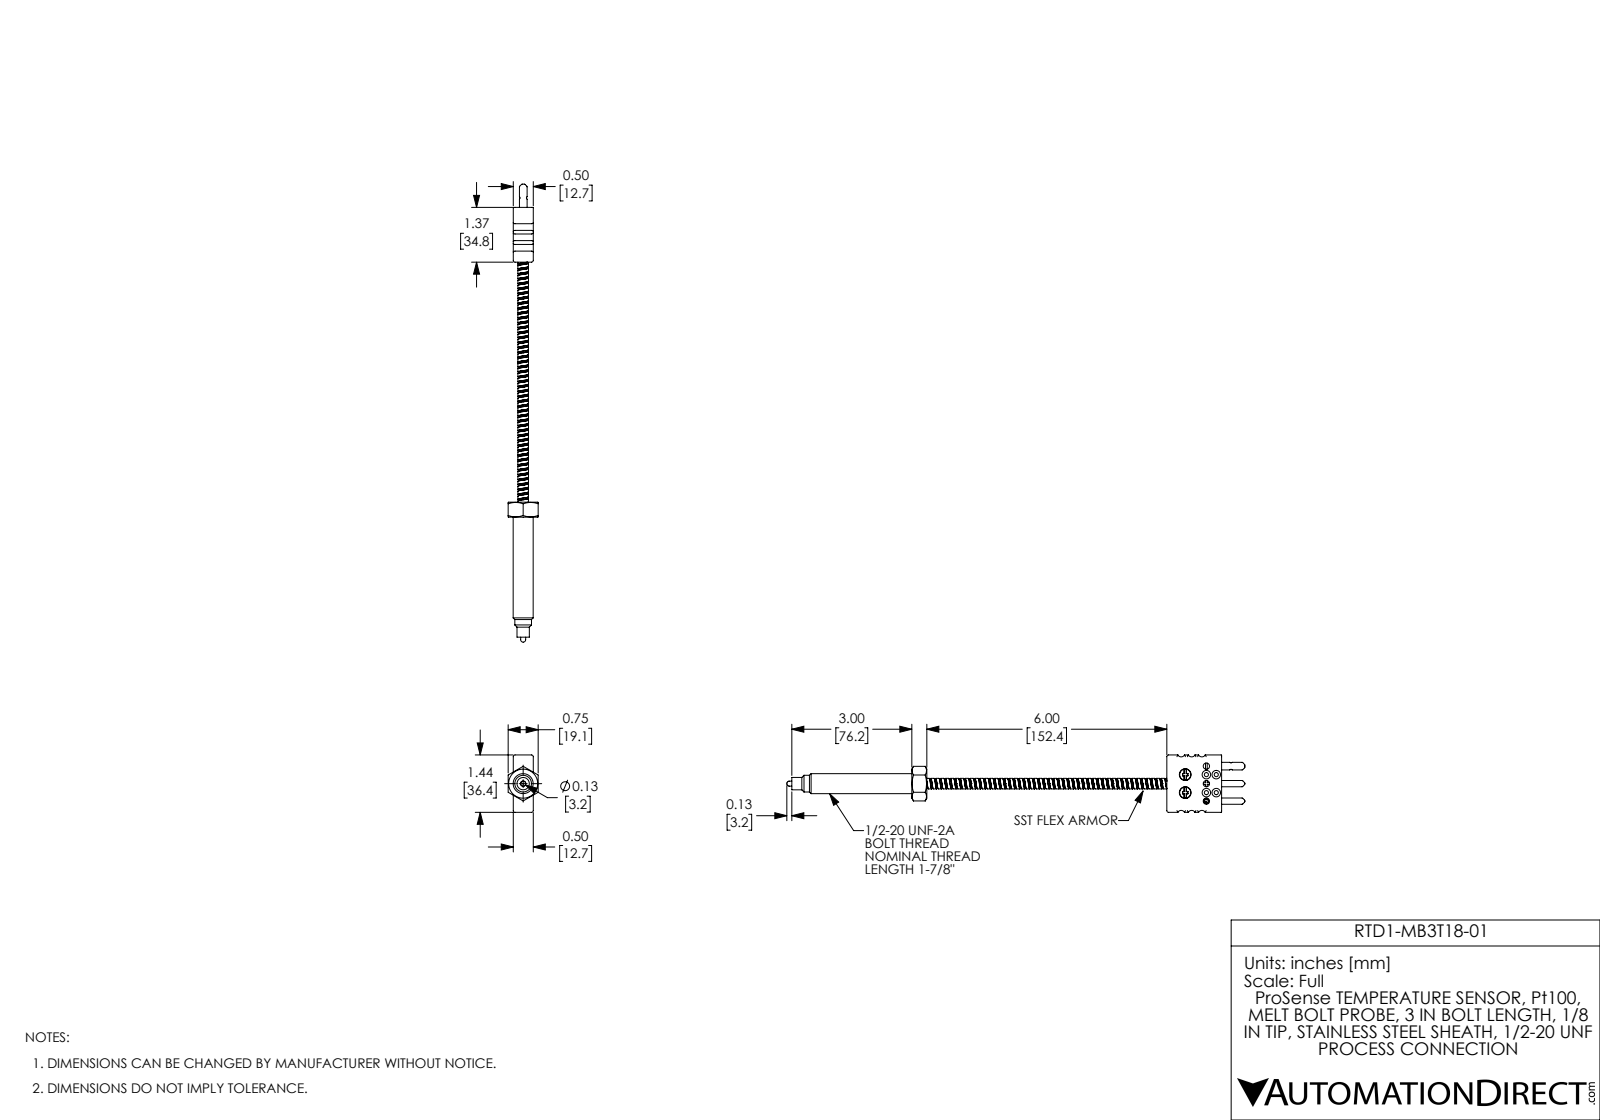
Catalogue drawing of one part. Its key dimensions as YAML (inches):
part_name: "RTD1-MB3T18-01"
step_written_by: "SolidWorks 2017 (AUTOMOTIVE_DESIGN)"
units: inches
bodies: {solids: 3, faces: 412, planar: 106, cylindrical: 190, other: 116}
overall_size: [11.451, 1.435, 0.75]
volume: 1.98
surface_area: 21.79
round_holes:
  - {diameter: 0.103, count: 4}
  - {diameter: 0.158, count: 3}
  - {diameter: 0.185, count: 2}
  - {diameter: 0.294, count: 2}
  - {diameter: 0.135, count: 1}
  - {diameter: 0.308, count: 1}
round_bosses_or_shafts:
  - {diameter: 0.278, count: 2}
  - {diameter: 0.156, count: 2}
  - {diameter: 0.102, count: 2}
  - {diameter: 0.5, count: 1}
  - {diameter: 0.417, count: 1}
  - {diameter: 0.309, count: 1}
  - {diameter: 0.265, count: 1}
  - {diameter: 0.191, count: 1}
partial_cylinders:
  - {radius: 0.045, count: 8}
  - {radius: 0.095, count: 6}
  - {radius: 0.01, count: 4}
face_to_face_distances: [0.5, 1.369, 0.75, 7.369, 6, 1.435, 7.744, 6.375, 0.375, 0.622]
hole_center_spacings: [0.529, 0.57, 0.776, 0.212, 0.225, 0.247, 0.326, 0.334]
